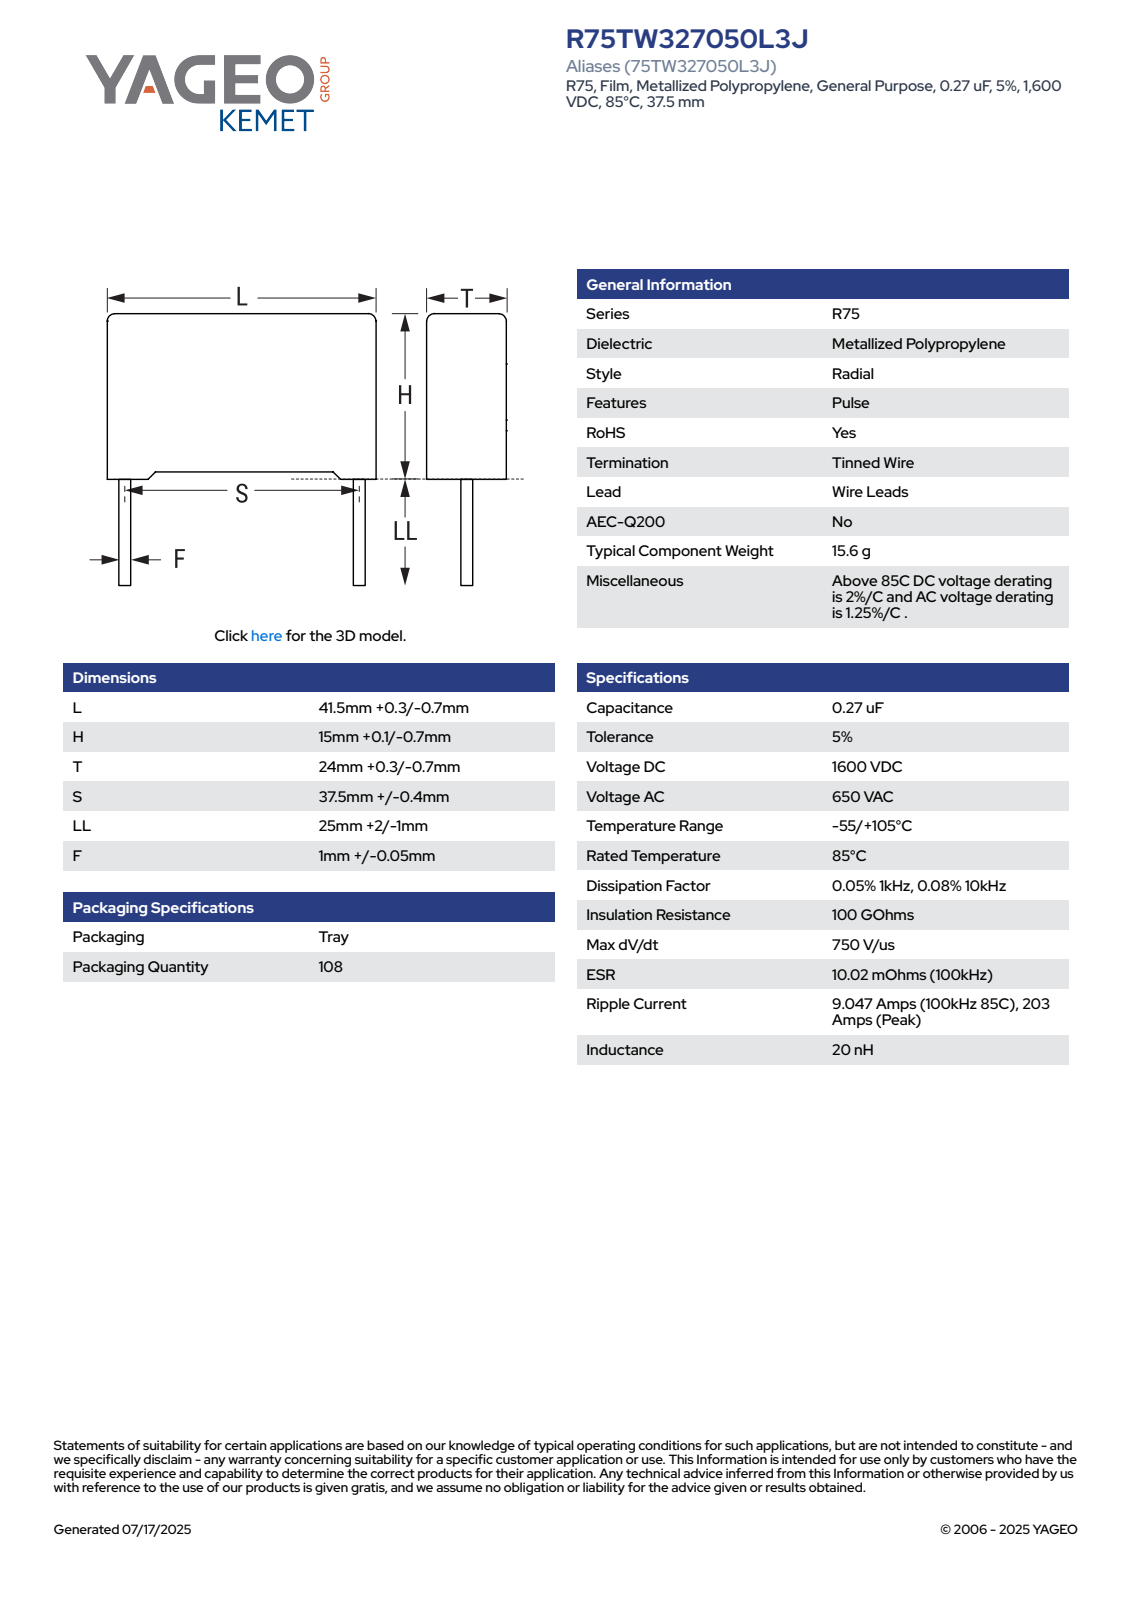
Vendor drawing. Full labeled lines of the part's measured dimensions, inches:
Part name (STEP PRODUCT): CFR_RB2_41.5X15X24_L41.8H15.1T24.3S37.5LL27F1.05
STEP written by: SolidWorks 2021 (AUTOMOTIVE_DESIGN)
Units: inches
Bodies: 4 solids, 85 faces (77 planar, 8 cylindrical, 0 other)
Overall size (bounding box): 1.657 × 1.646 × 0.957
Volume: 0.897 in³ · Surface area: 6.719 in²
Round bosses / shafts (diameter × count): ⌀0.041 ×2
Partial cylindrical surfaces — rounded edges, fillets, slot ends (radius × count): R0.02 ×4
Main face-to-face distances: 0.565, 0.957, 1.646, 0.574, 0.02, 0.03, 0.594, 0.055, 1.591, 0.957
